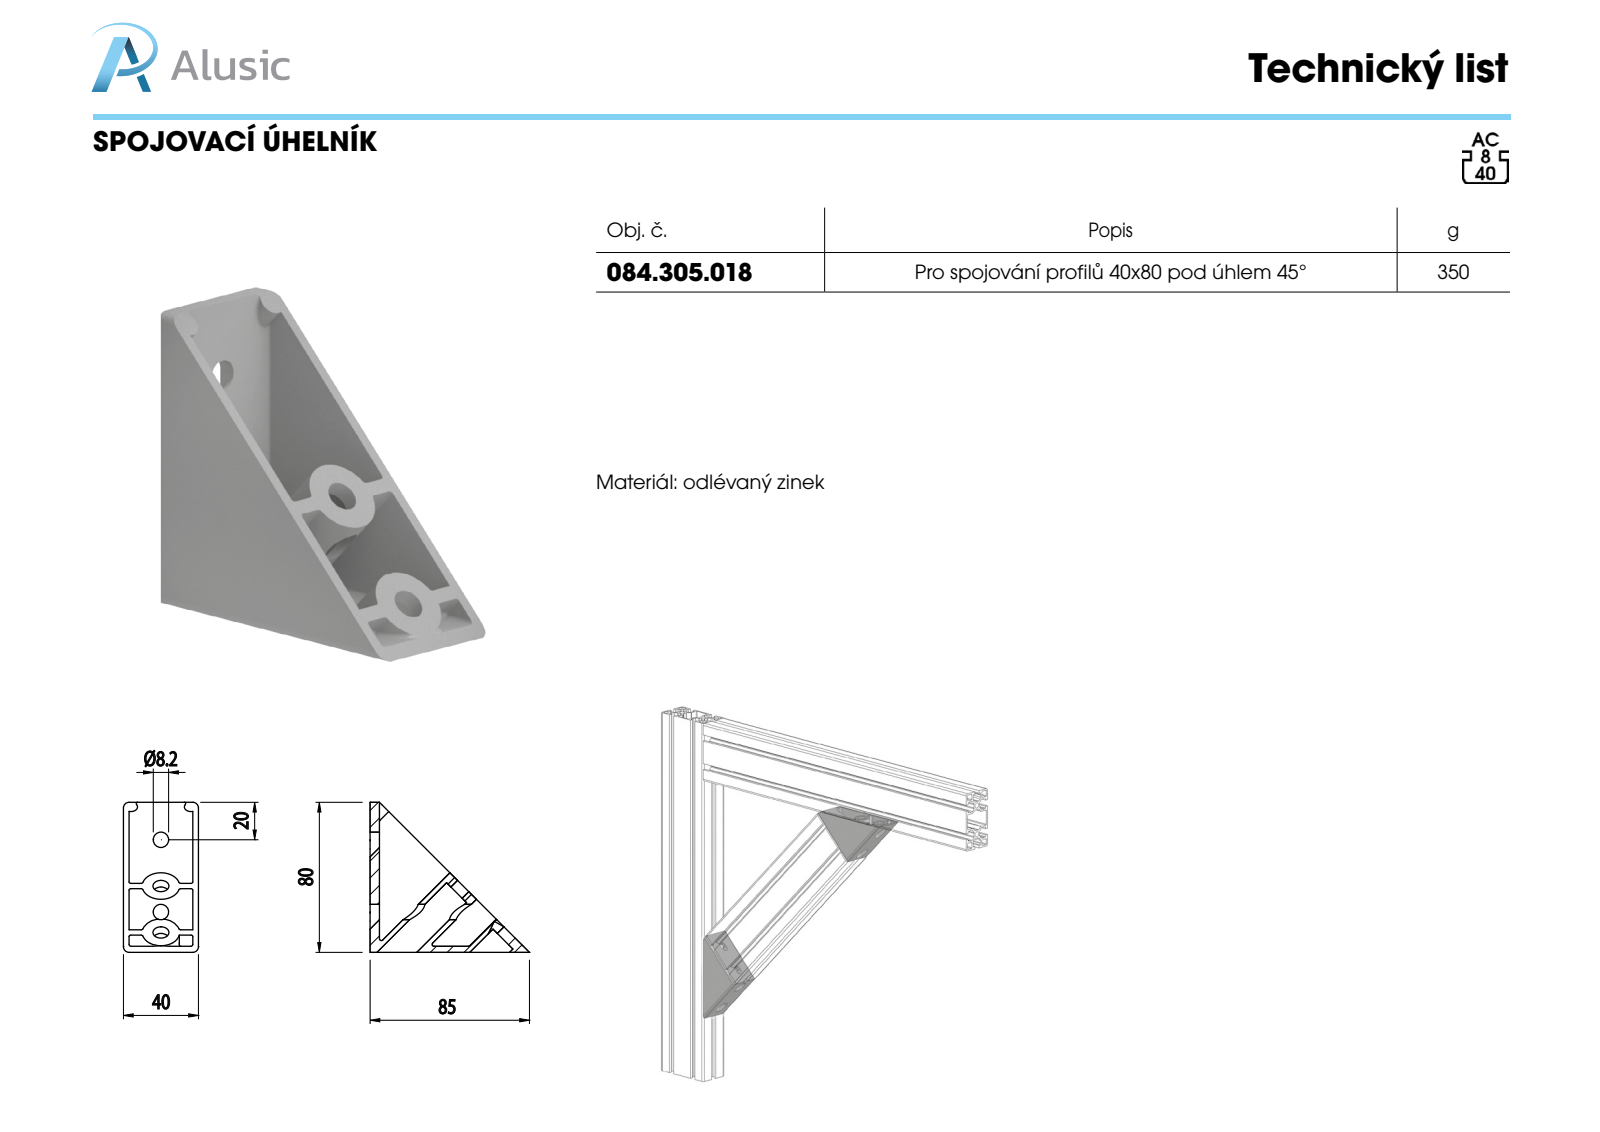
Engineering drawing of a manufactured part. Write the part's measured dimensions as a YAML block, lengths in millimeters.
part_name: "084.305.018"
step_written_by: "SolidWorks 2011 (CONFIG_CONTROL_DESIGN)"
units: millimeters
bodies: {solids: 1, faces: 144, planar: 28, cylindrical: 73, other: 43}
overall_size: [85, 80.12, 40]
volume: 52899
surface_area: 31363
round_holes:
  - {diameter: 8.5, count: 2}
  - {diameter: 15, count: 2}
  - {diameter: 8.2, count: 1}
round_bosses_or_shafts:
  - {diameter: 20, count: 1}
partial_cylinders:
  - {radius: 1, count: 22}
  - {radius: 3, count: 6}
  - {radius: 4.1, count: 3}
  - {radius: 3.5, count: 2}
  - {radius: 10, count: 1}
face_to_face_distances: [3, 37, 40, 34, 5, 3.25, 4, 4.99, 35, 80]
hole_center_spacings: [35, 34.99, 35.01]
